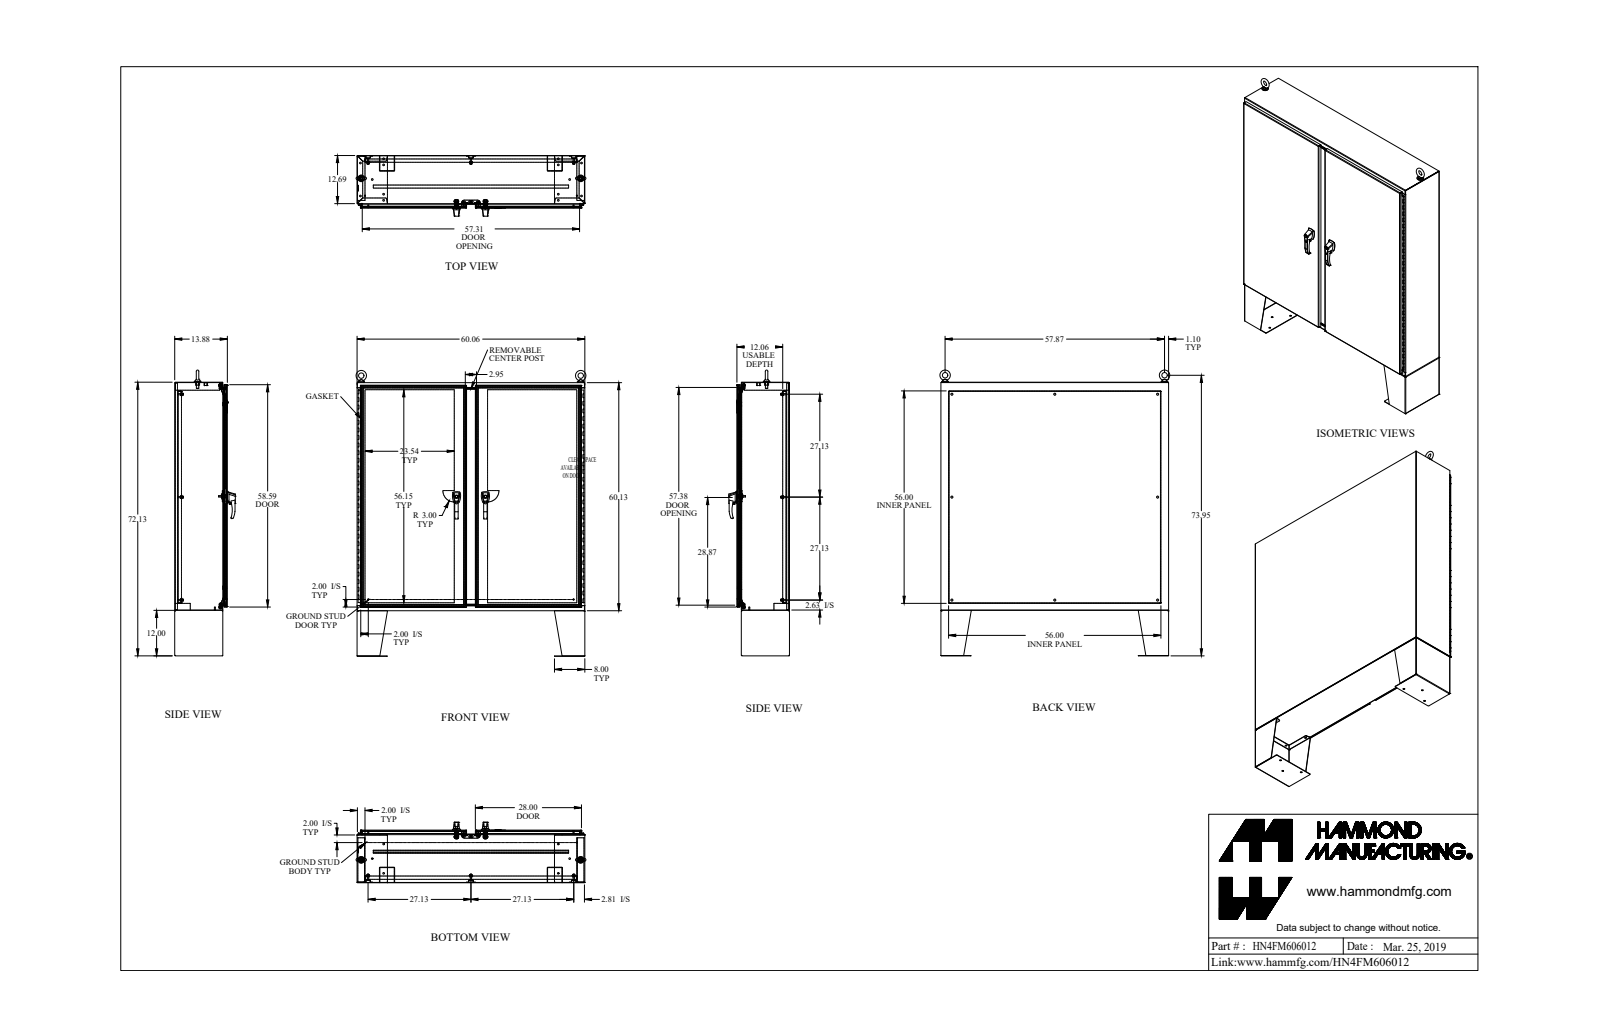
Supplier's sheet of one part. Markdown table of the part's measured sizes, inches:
| quantity | value |
| --- | --- |
| part name | HN4FM606012 |
| STEP written by | SolidWorks 2018 (AUTOMOTIVE_DESIGN) |
| units | inches |
| bodies | 130 solids, 3768 faces (1736 planar, 1659 cylindrical, 373 other) |
| overall size | 75.315 × 60.607 × 15.99 |
| volume | 1 748 in³ |
| surface area | 34 928 in² |
| round holes (diameter × count) | 0.304 × 20, 0.437 × 14, 0.307 × 8, 0.35 × 8, 0.563 × 8, 0.25 × 6, 0.445 × 6, 0.281 × 4, 0.313 × 4, 0.39 × 4, 0.201 × 3, 0.313 × 3 |
| round bosses / shafts (diameter × count) | 1 × 10, 0.65 × 8, 0.375 × 8, 0.33 × 8, 0.281 × 8, 0.75 × 4, 0.625 × 4, 0.44 × 4 |
| partial cylindrical surfaces (radius × count) | 0.5 × 33, 0.018 × 32, 0.125 × 32, 0.06 × 28, 0.048 × 27, 0.143 × 27, 0.03 × 12, 0.09 × 12 |
| main face-to-face distances | 0.095, 13.78, 13.685, 11.998, 0.125, 13.875, 1.782, 1.687, 12.093, 1.657 |
| hole center spacings | 6, 12, 18, 24, 54.25, 30, 58.513, 1.61 |
